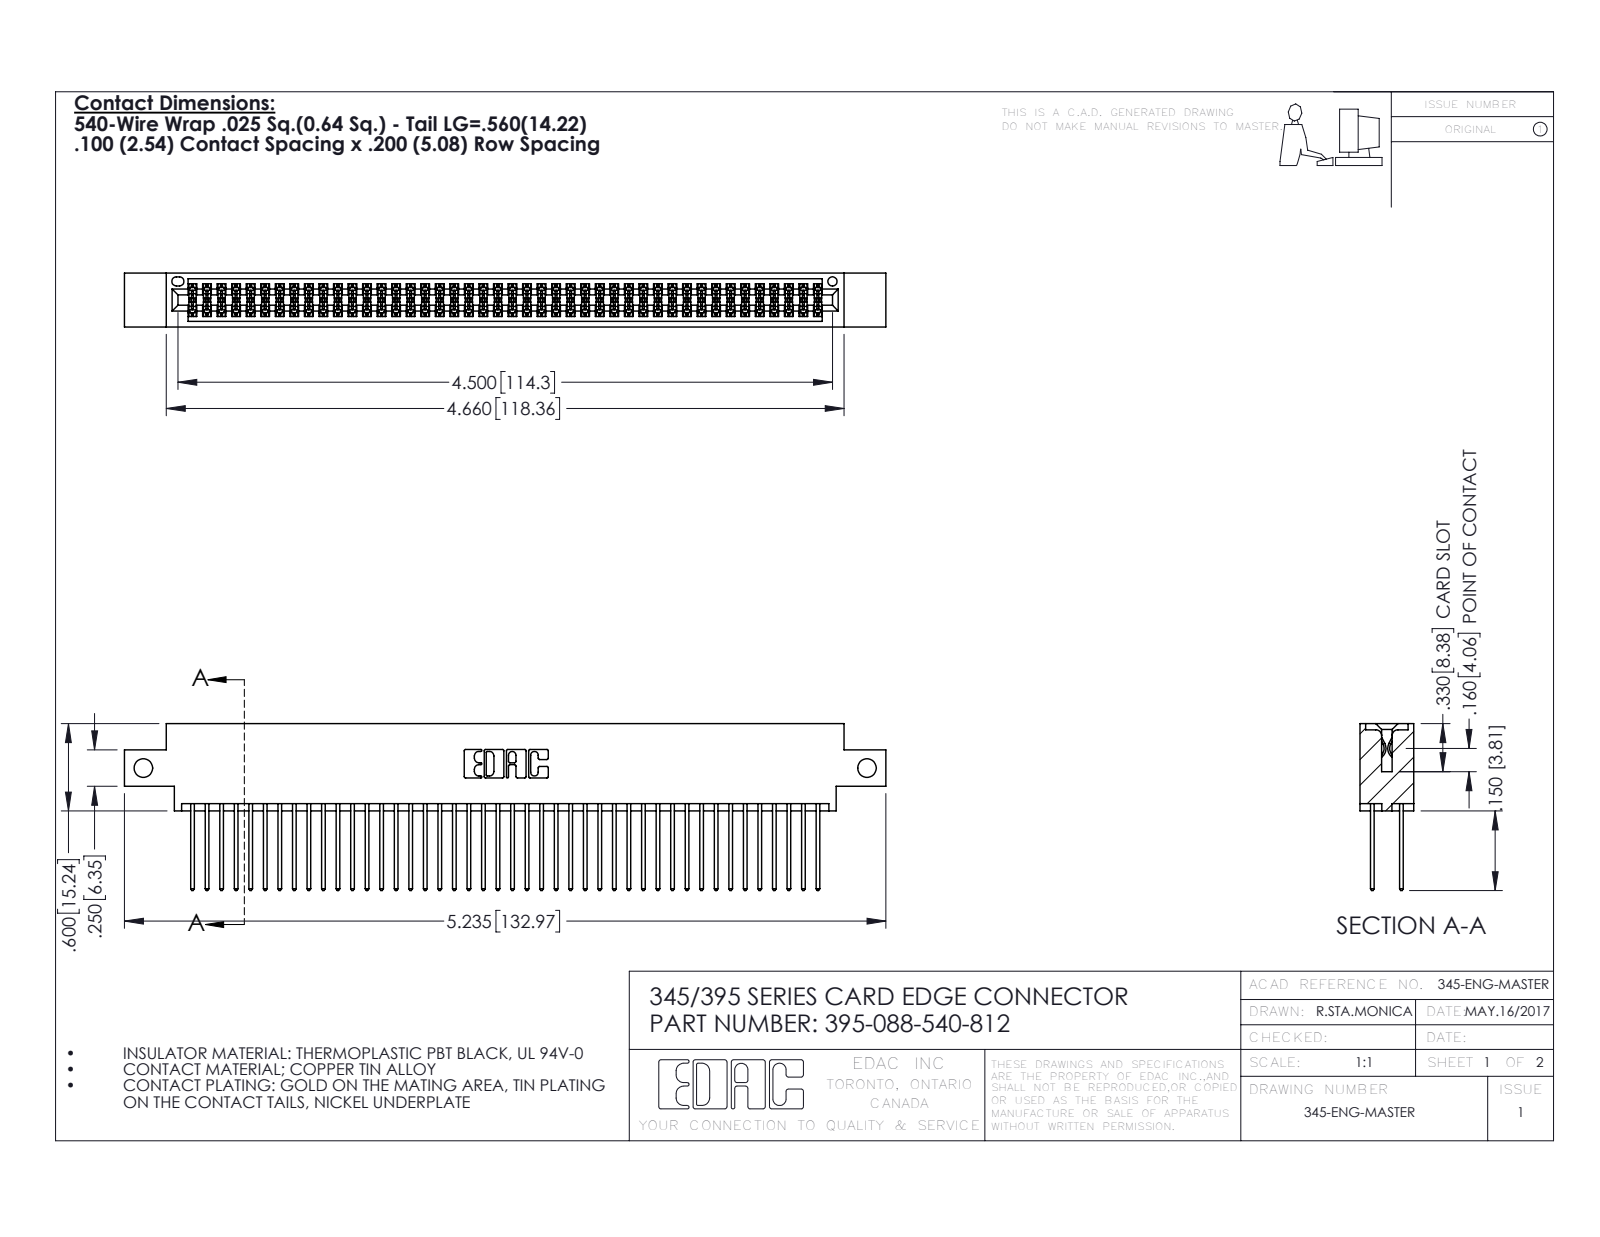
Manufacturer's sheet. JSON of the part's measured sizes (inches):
{"part_name": "345-292-001_345-293-140; 345 Part_0.170 Offset - Side Mount; 395-088-540-812", "step_written_by": "SolidWorks 2016 (CONFIG_CONTROL_DESIGN)", "units": "inches", "bodies": {"solids": 89, "faces": 4530, "planar": 2988, "cylindrical": 1542, "other": 0}, "overall_size": [5.235, 1.147, 0.37], "volume_in3": 0.797, "surface_area_in2": 32.41, "round_holes": [[0.128, 2], [0.064, 1]], "partial_cylinders_radius": [[0.006, 132], [0.01, 88], [0.01, 22], [0.007, 6], [0.031, 6], [0.026, 3], [0.014, 2], [0.019, 2]], "face_to_face_distances": [0.298, 0.072, 0.2, 0.098, 0.272, 0.025, 0.37, 0.225, 0.175, 0.149], "hole_center_spacings": [4.975]}
